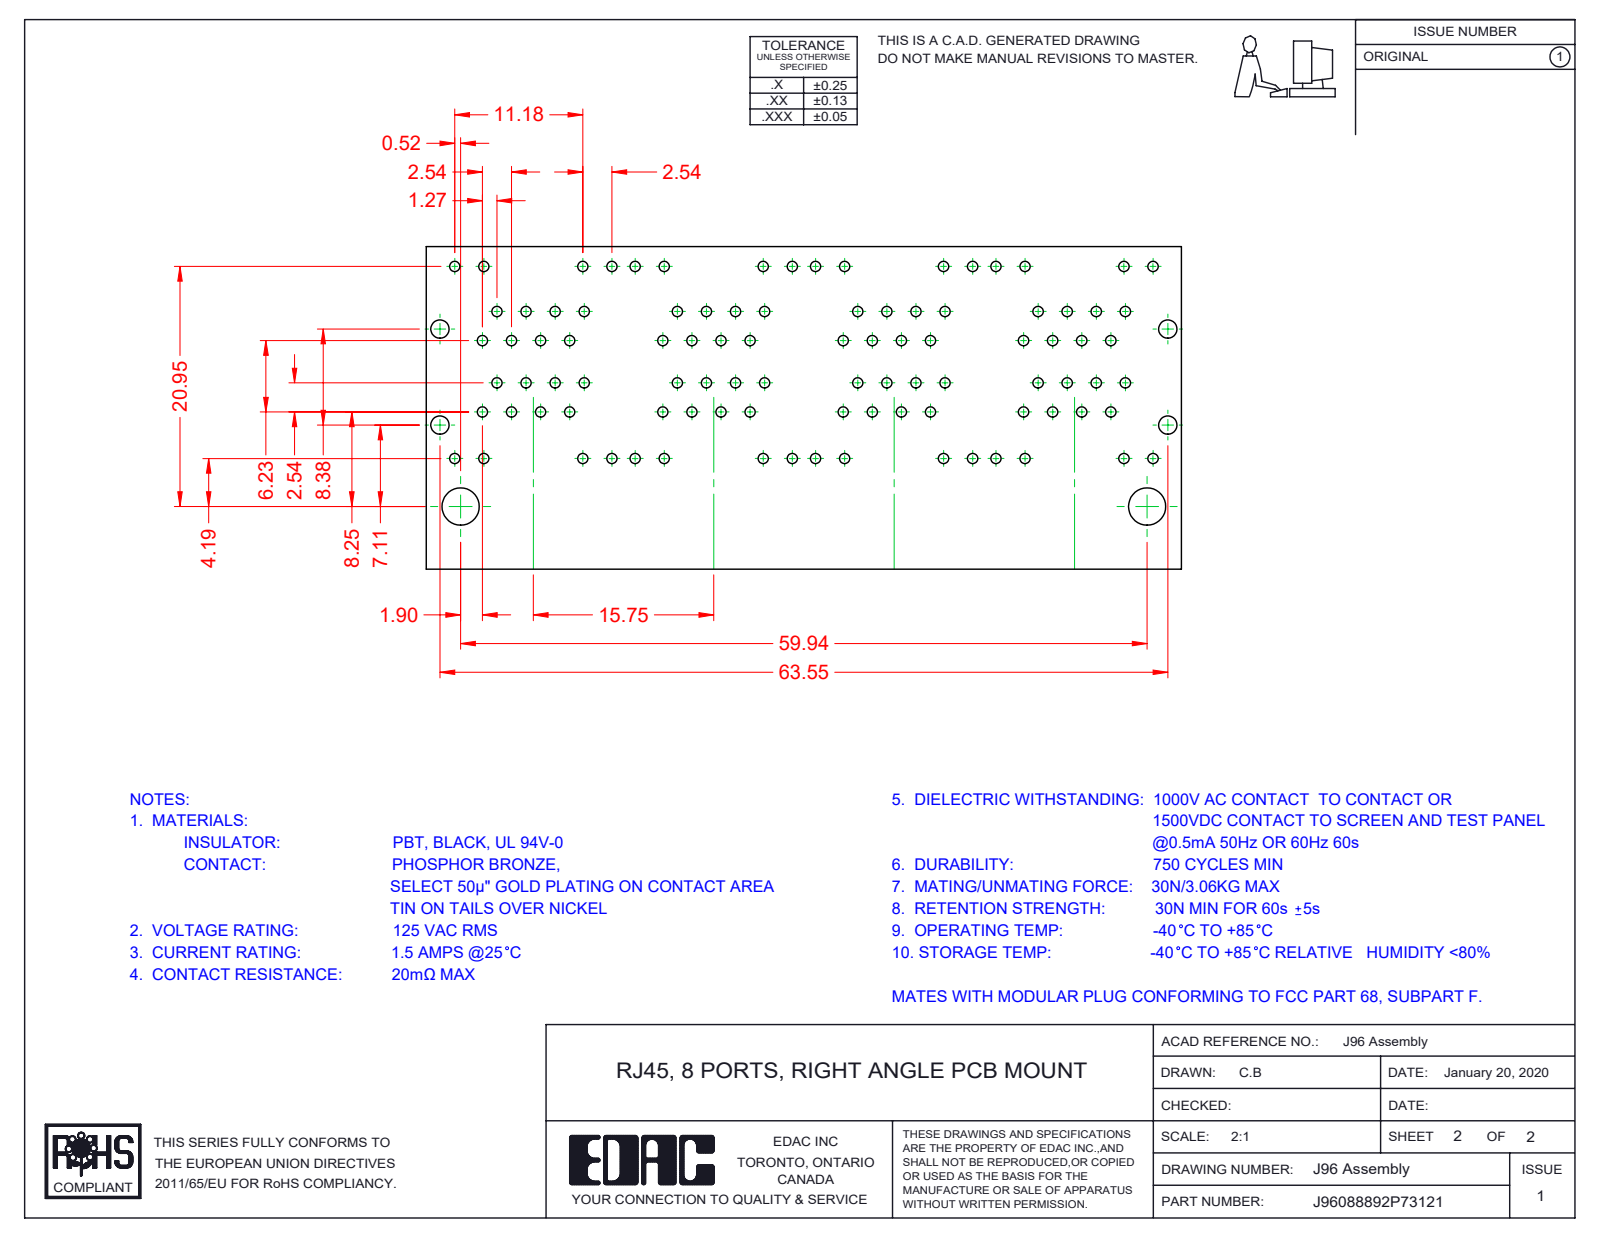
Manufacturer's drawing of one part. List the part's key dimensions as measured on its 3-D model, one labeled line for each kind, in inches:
Part name (STEP PRODUCT): 96 Insulator Insert; J96088892P73121; 96 Insulator_8 Ports; 96 LED RH Lower_3-Green (+8 more)
STEP written by: SolidWorks 2016 (CONFIG_CONTROL_DESIGN)
Units: inches
Bodies: 96 solids, 7658 faces (6069 planar, 1323 cylindrical, 266 other)
Overall size (bounding box): 2.522 × 1.165 × 1.129
Volume: 1.474 in³ · Surface area: 98.67 in²
Round holes (diameter × count): ⌀0.067 ×3
Round bosses / shafts (diameter × count): ⌀0.066 ×3
Partial cylindrical surfaces — rounded edges, fillets, slot ends (radius × count): R0.01 ×124, R0.014 ×73, R0.039 ×72, R0.02 ×49, R0.036 ×32, R0.008 ×21, R0.028 ×11, R0.009 ×8
Main face-to-face distances: 0.62, 0.014, 0.392, 0.046, 0.063, 0.021, 0.393, 0.401, 0.499, 0.133
Hole centre spacings: 0.62, 1.24
